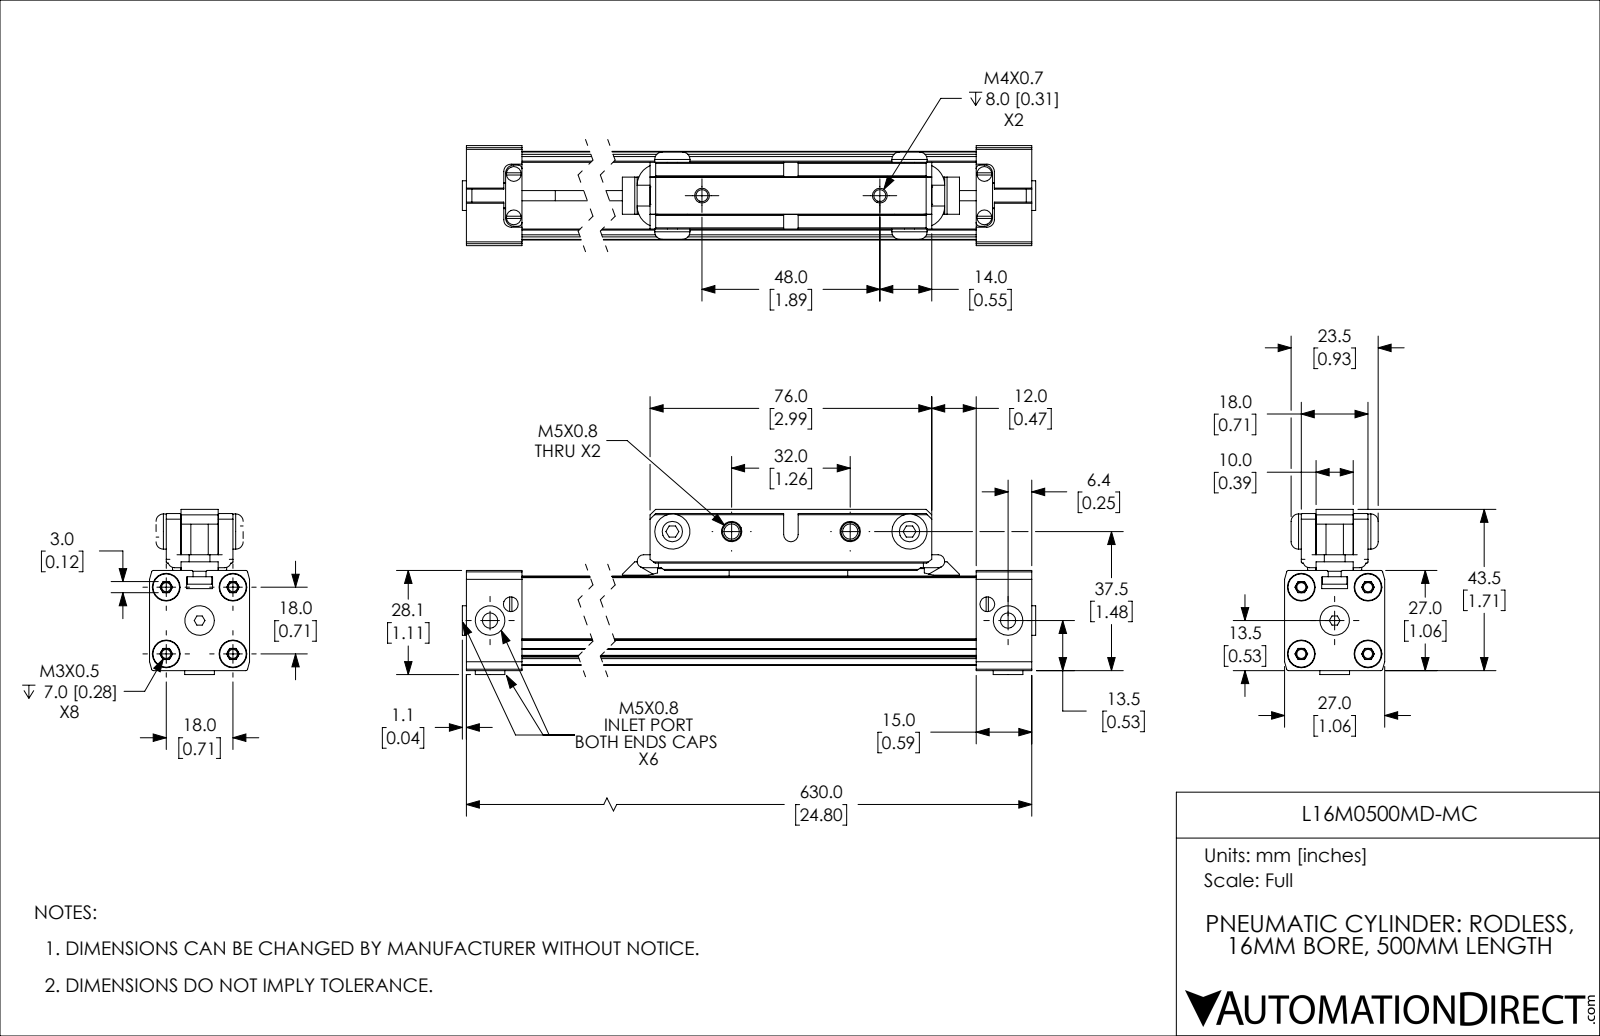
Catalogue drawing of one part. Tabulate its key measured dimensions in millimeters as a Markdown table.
| quantity | value |
| --- | --- |
| part name | L16M0500MD-MC_PISTON; L16M0500MD-MC; L16M0500MD-MC_BODY |
| STEP written by | SolidWorks 2019 (CONFIG_CONTROL_DESIGN) |
| units | millimeters |
| bodies | 13 solids, 827 faces (435 planar, 284 cylindrical, 108 other) |
| overall size | 632.15 × 44.57 × 27 |
| volume | 257 190 mm³ |
| surface area | 133 243 mm² |
| round holes (diameter × count) | 4.13 × 9, 4 × 6, 8 × 5, 2.46 × 4, 5.5 × 4, 7.5 × 4, 3.24 × 2, 16.1 × 1 |
| round bosses / shafts (diameter × count) | 7.2 × 4, 3.5 × 4, 5 × 3, 3.8 × 3, 9.5 × 2, 16 × 1 |
| partial cylindrical surfaces (radius × count) | 0.3 × 22, 0.5 × 14, 0.25 × 8, 0.62 × 6, 1 × 6, 0.2 × 4, 0.6 × 4, 2 × 4 |
| main face-to-face distances | 23.9, 24, 10.58, 13.32, 20.95, 2.95, 7.63, 10.37, 1.5, 25.5 |
| hole center spacings | 8.67, 12.73, 18, 610.83, 48, 7.12, 11.7, 11.91 |
